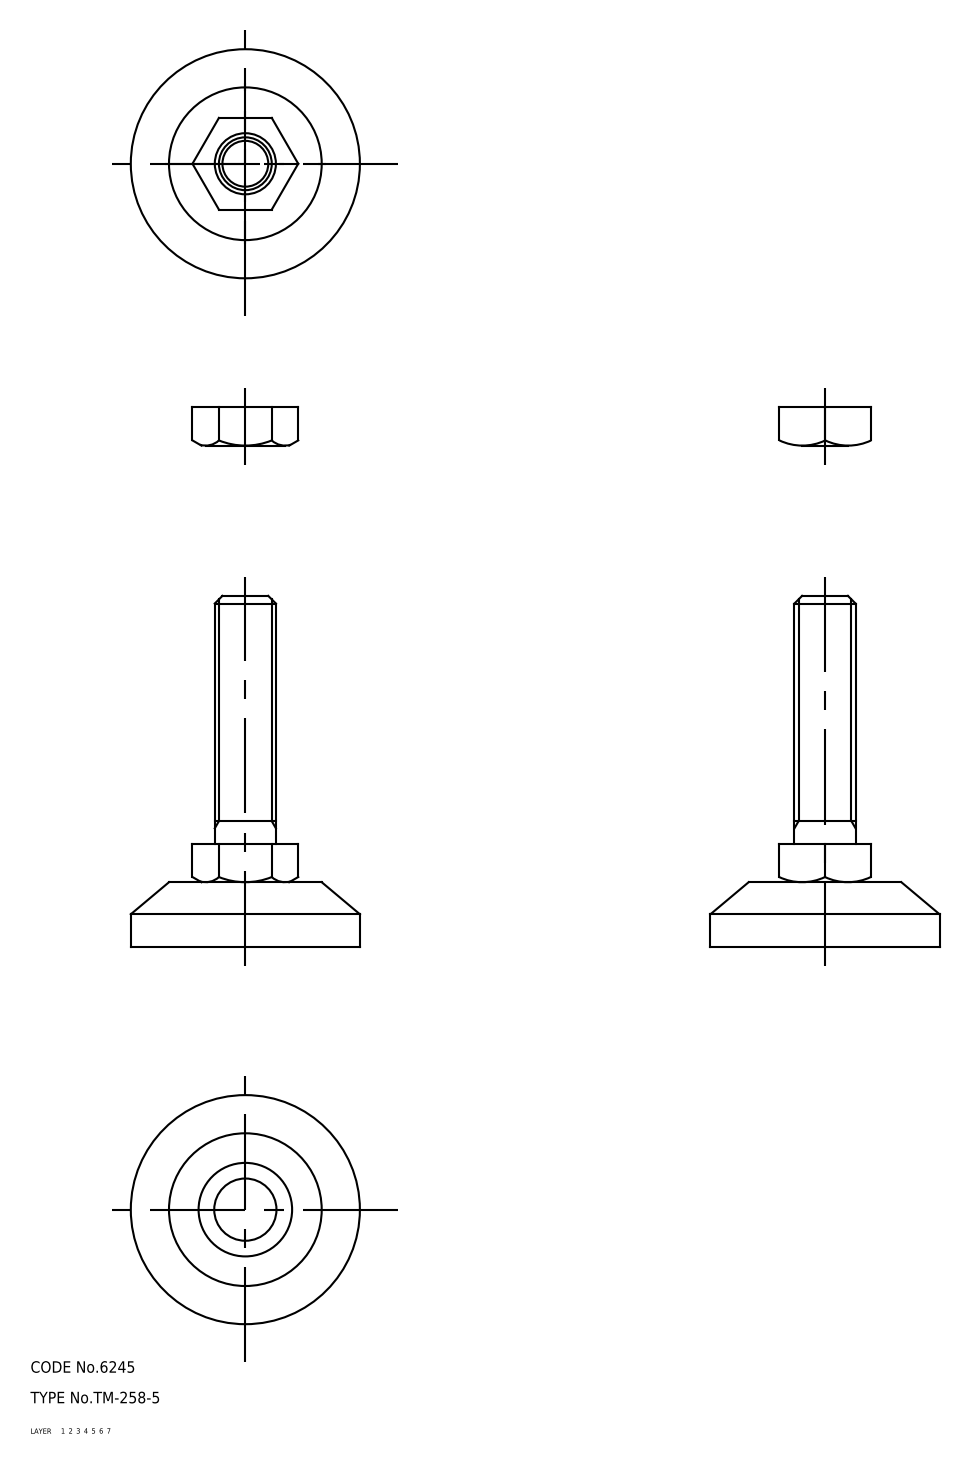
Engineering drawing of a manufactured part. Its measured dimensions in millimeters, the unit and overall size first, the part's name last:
Units: millimetres
Overall size (bounding box): 92 × 60 × 60
Volume: 53 048 mm³ · Surface area: 16 318 mm²
Bodies: 3 solids, 67 faces (0 planar, 0 cylindrical, 67 other)
Part name (STEP PRODUCT): 67112304; 67112317; 67112330
STEP written by: CADfix (AUTOMOTIVE_DESIGN)
